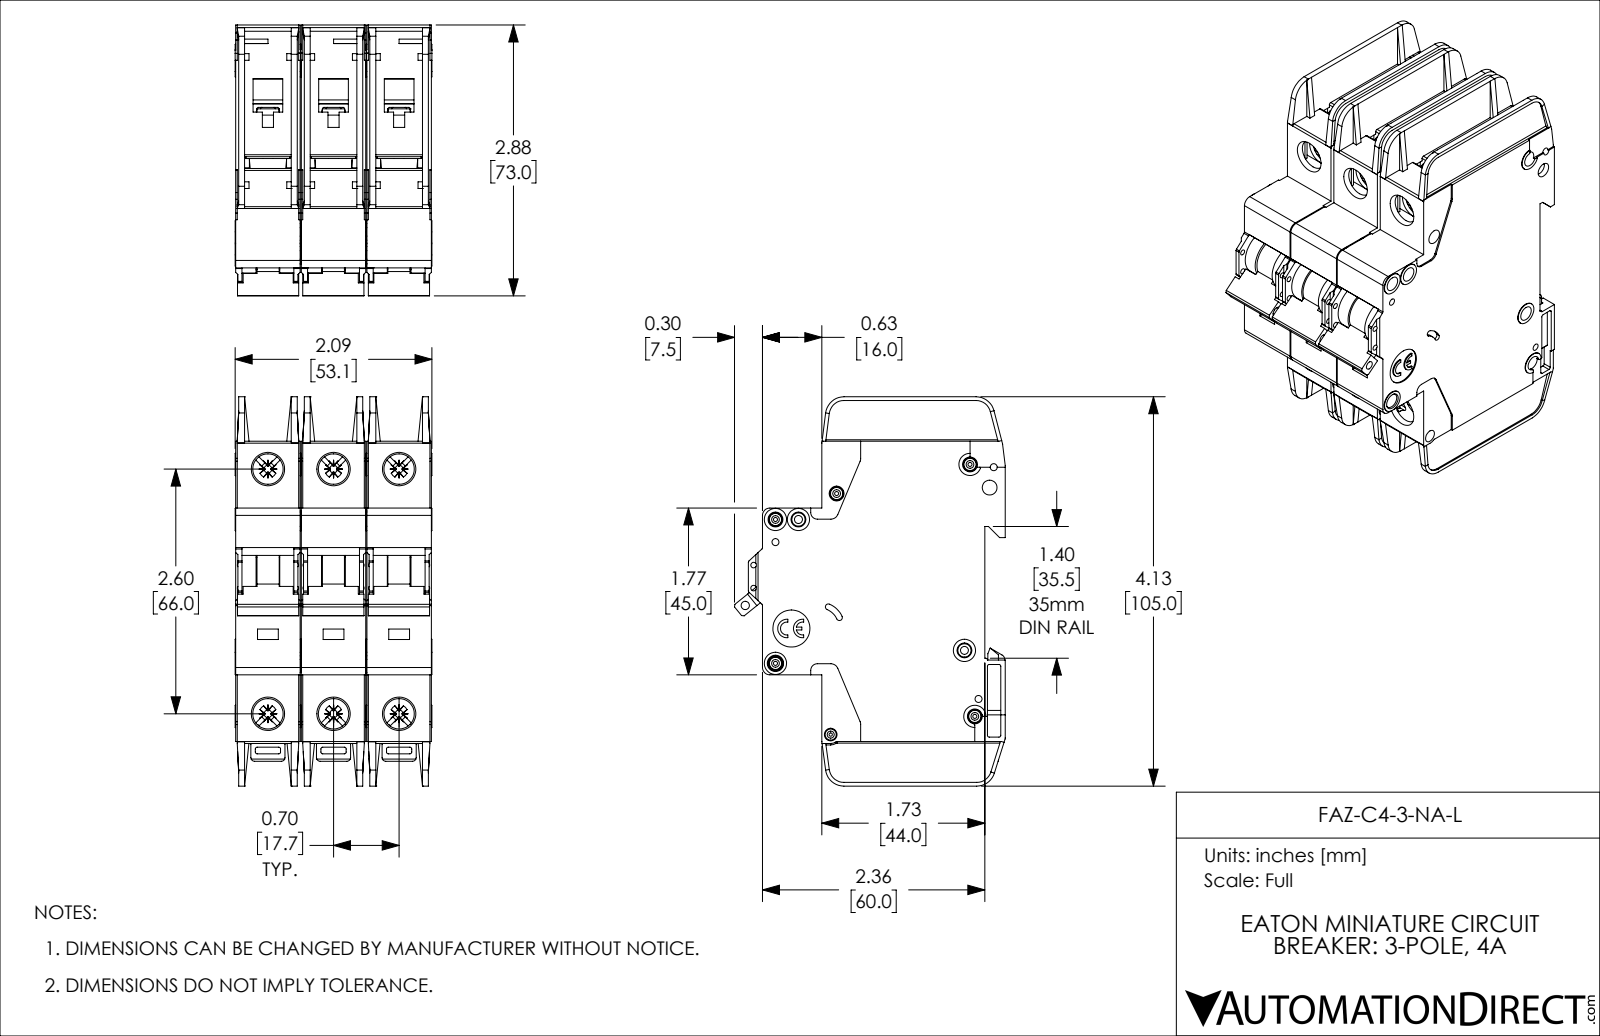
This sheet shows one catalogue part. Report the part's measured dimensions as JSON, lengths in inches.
{"part_name": "FAZ-C4-3-NA-L", "step_written_by": "SolidWorks 2019 (AUTOMOTIVE_DESIGN)", "units": "inches", "bodies": {"solids": 3, "faces": 3381, "planar": 2013, "cylindrical": 1071, "other": 297}, "overall_size": [4.134, 2.876, 2.091], "volume_in3": 14.05, "surface_area_in2": 123, "round_holes": [[0.157, 8], [0.323, 6], [0.043, 5], [0.075, 4], [0.059, 2], [0.085, 2], [0.035, 1], [0.089, 1], [0.098, 1], [0.134, 1], [0.394, 1]], "round_bosses_or_shafts": [[0.13, 5], [0.236, 4], [0.118, 4], [0.098, 3]], "partial_cylinders_radius": [[0.02, 72], [0.016, 30], [0.039, 18], [0.043, 12], [0.079, 12], [0.008, 6], [0.01, 6], [0.028, 6]], "face_to_face_distances": [0.697, 0.047, 1.394, 0.685, 0.591, 1.382, 0.744, 0.65, 0.106, 0.094], "hole_center_spacings": [0.697, 2.69, 2.598, 0.244, 0.537, 0.87, 1.394, 2.948]}
